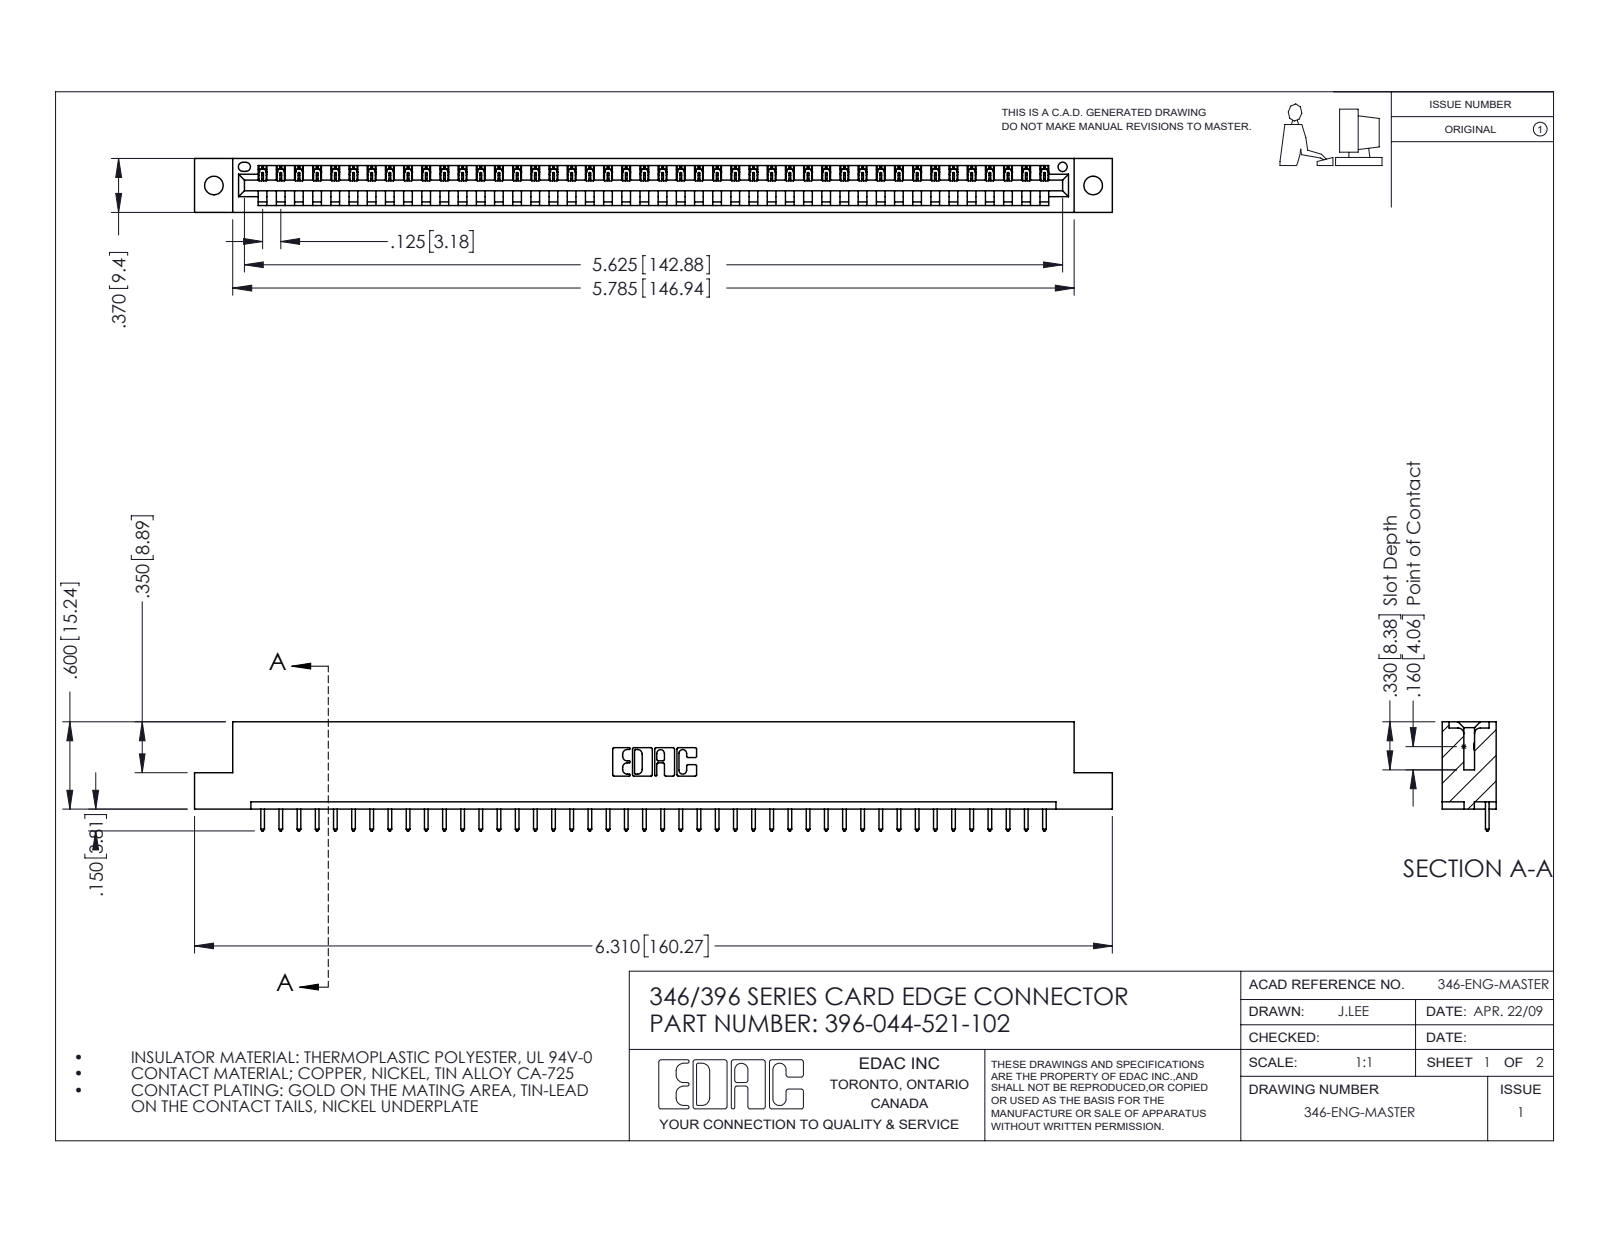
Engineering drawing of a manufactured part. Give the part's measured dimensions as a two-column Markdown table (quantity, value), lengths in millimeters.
| quantity | value |
| --- | --- |
| part name | 345-292-001_345-293-121; 346 Part_Flush Mounting Lugs - 0.128 Dia; 396-044-521-102 |
| STEP written by | SolidWorks 2016 (CONFIG_CONTROL_DESIGN) |
| units | millimeters |
| bodies | 45 solids, 2674 faces (1836 planar, 838 cylindrical, 0 other) |
| overall size | 160.3 × 19.1 × 9.4 |
| volume | 15 200 mm³ |
| surface area | 18 250 mm² |
| round holes (diameter × count) | 3.3 × 2, 1.6 × 1 |
| partial cylindrical surfaces (radius × count) | 0.2 × 88, 0.3 × 88, 0.3 × 22, 0.2 × 6, 0.8 × 6, 0.7 × 3, 0.8 × 2, 1 × 2 |
| main face-to-face distances | 1.2, 8.2, 9.4, 6.4, 1.8, 7.6, 0.6, 3.8, 5.6, 2.5 |
| hole center spacings | 6.2, 148.2, 153.5 |
